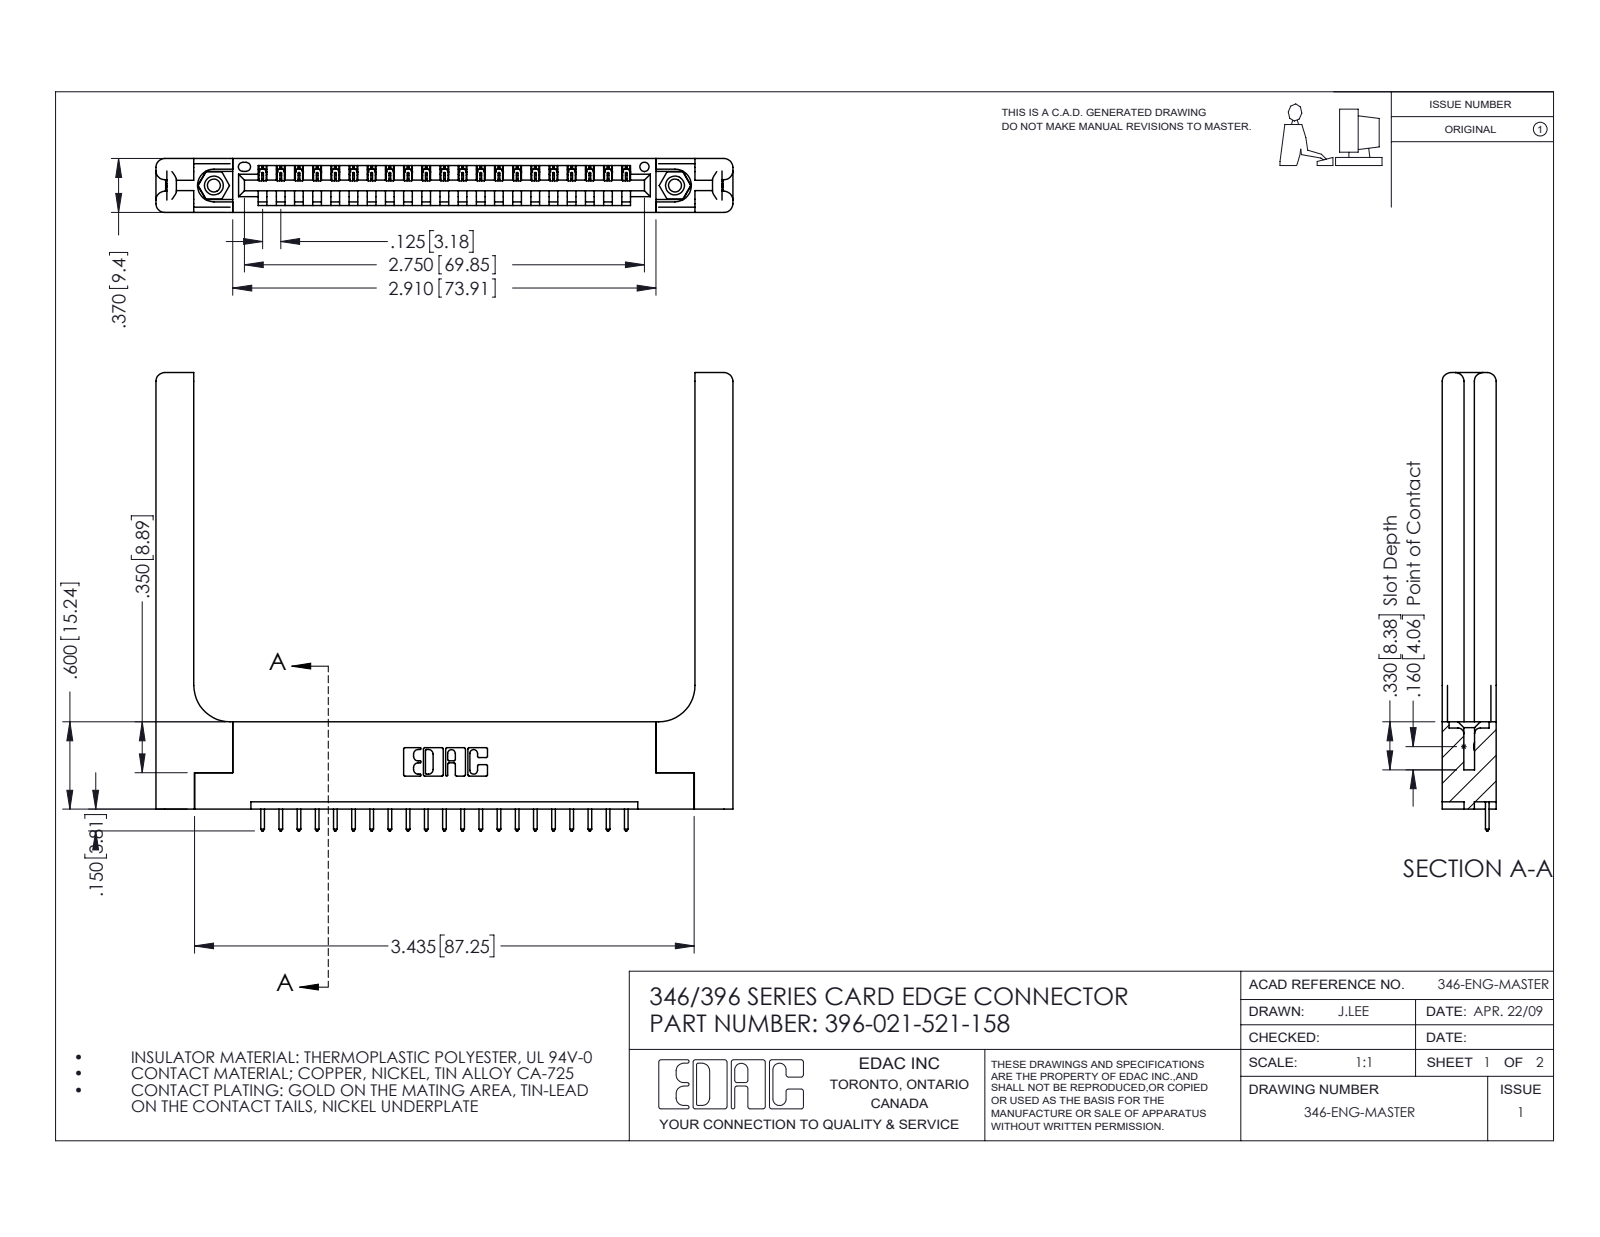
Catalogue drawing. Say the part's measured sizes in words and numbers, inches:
The part is named "346-220-058_345-220-058; 345-250-001_345-250-001-102; 396-021-521-158; 346 Part_Flush Mounting Lugs - 0.156 Dia-TH (+1 more)". Its 3-D file was written by "SolidWorks 2016 (CONFIG_CONTROL_DESIGN)". It is 26 solids with 1596 faces: 1064 planar, 472 cylindrical and 60 other. Overall it measures 3.966 by 3.15 by 0.37 inches. Its volume is 1.035 cubic inches and its surface area 25.58 square inches. Round holes: 2 of diameter 0.089, 2 of diameter 0.125, 2 of diameter 0.156, 1 of diameter 0.064. Round bosses or shafts: 2 of diameter 0.155. Partial cylindrical surfaces (rounded edges, fillets, slot ends): 42 of radius 0.006, 42 of radius 0.01, 22 of radius 0.01, 16 of radius 0.06, 6 of radius 0.007, 6 of radius 0.031, 3 of radius 0.026, 2 of radius 0.03. The main face-to-face distances are 0.37, 0.072, 0.15, 0.148, 0.048, 0.322, 0.25, 0.102, 0.22, 0.173. The hole center spacings are 0.246, 2.963, 3.17.
